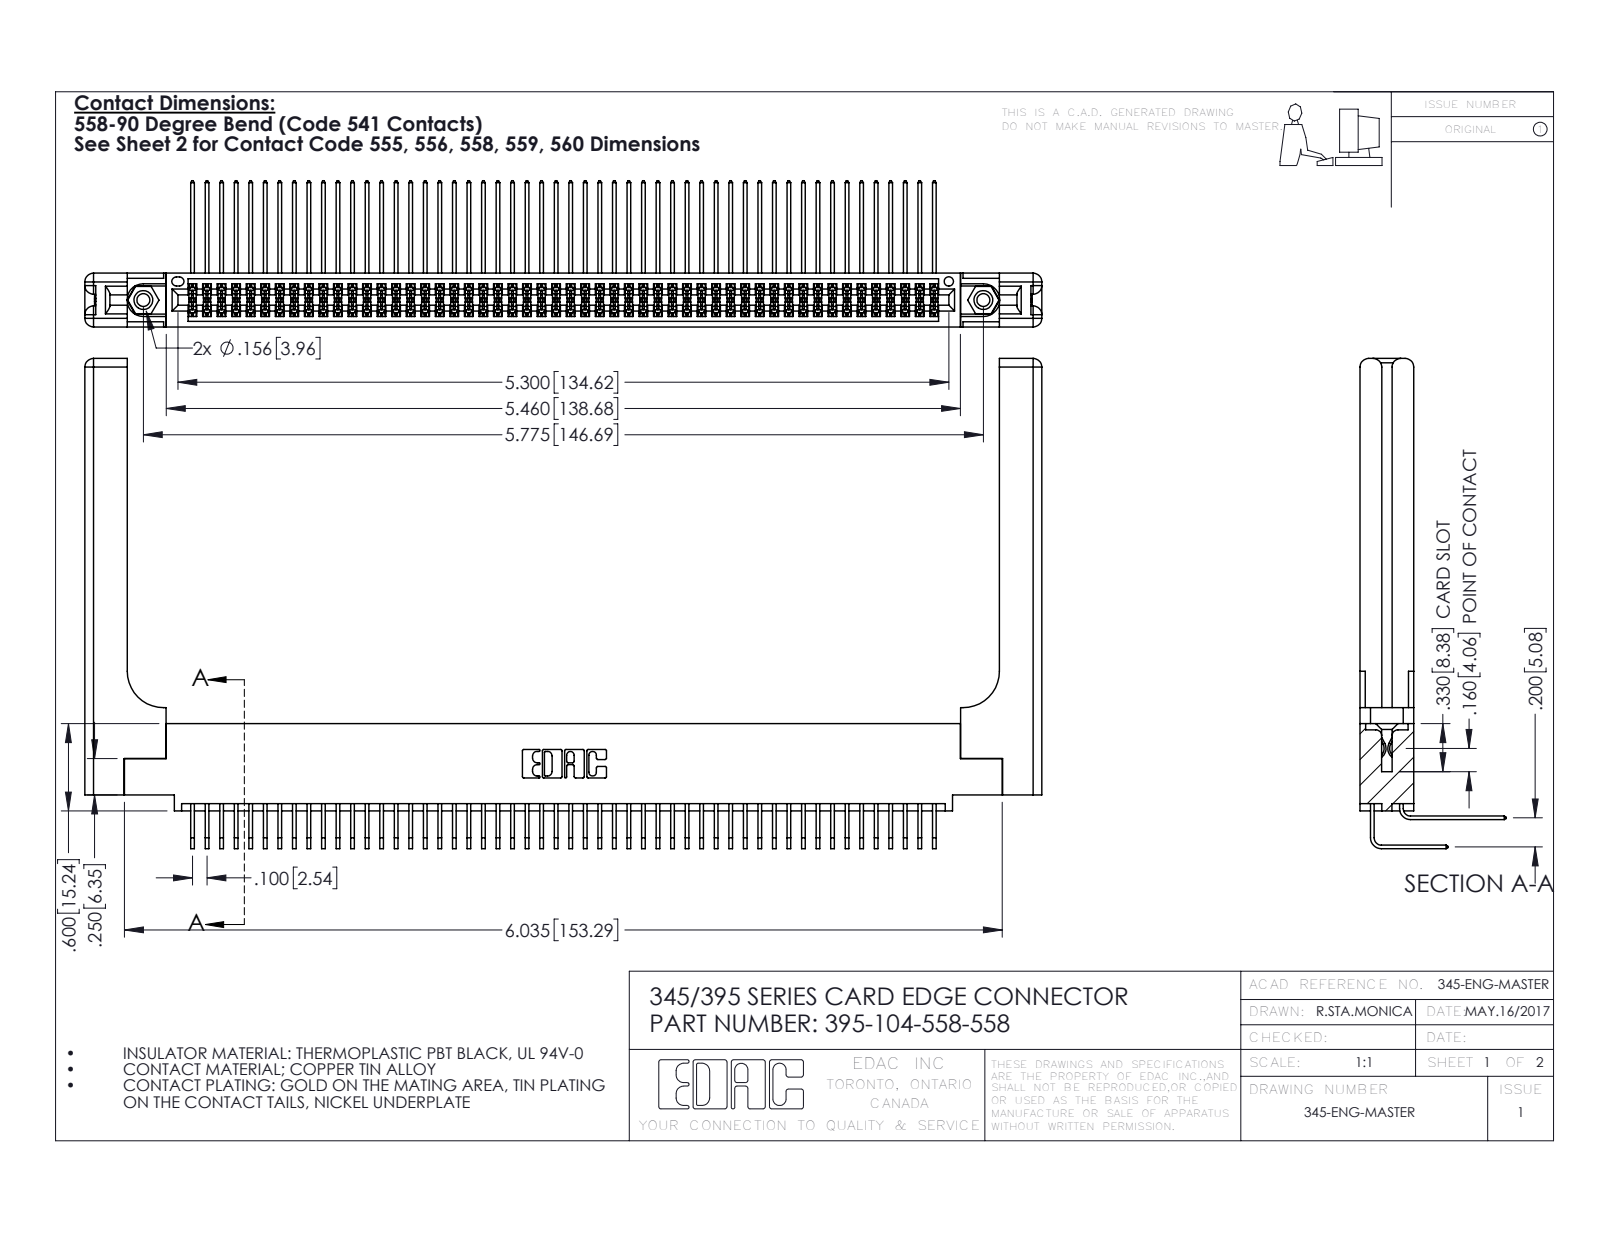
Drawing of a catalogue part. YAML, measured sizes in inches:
part_name: "345-220-058_345-220-058; 345-292-001_558 559 Tail - 1; 345-250-001_345-250-001-102; 345 Part_0.110 Offset - 0.156 Dia-TH (+2 more)"
step_written_by: "SolidWorks 2016 (CONFIG_CONTROL_DESIGN)"
units: inches
bodies: {solids: 109, faces: 5794, planar: 3872, cylindrical: 1862, other: 60}
overall_size: [6.579, 3.369, 1.005]
volume: 1.546
surface_area: 51.27
round_holes:
  - {diameter: 0.089, count: 2}
  - {diameter: 0.125, count: 2}
  - {diameter: 0.156, count: 2}
  - {diameter: 0.064, count: 1}
round_bosses_or_shafts:
  - {diameter: 0.155, count: 2}
partial_cylinders:
  - {radius: 0.006, count: 157}
  - {radius: 0.01, count: 22}
  - {radius: 0.06, count: 16}
  - {radius: 0.007, count: 6}
  - {radius: 0.031, count: 6}
  - {radius: 0.026, count: 3}
  - {radius: 0.014, count: 2}
  - {radius: 0.019, count: 2}
face_to_face_distances: [0.072, 0.298, 0.37, 0.2, 0.098, 0.272, 0.025, 0.225, 0.148, 0.15]
hole_center_spacings: [0.27, 5.539, 5.775]
